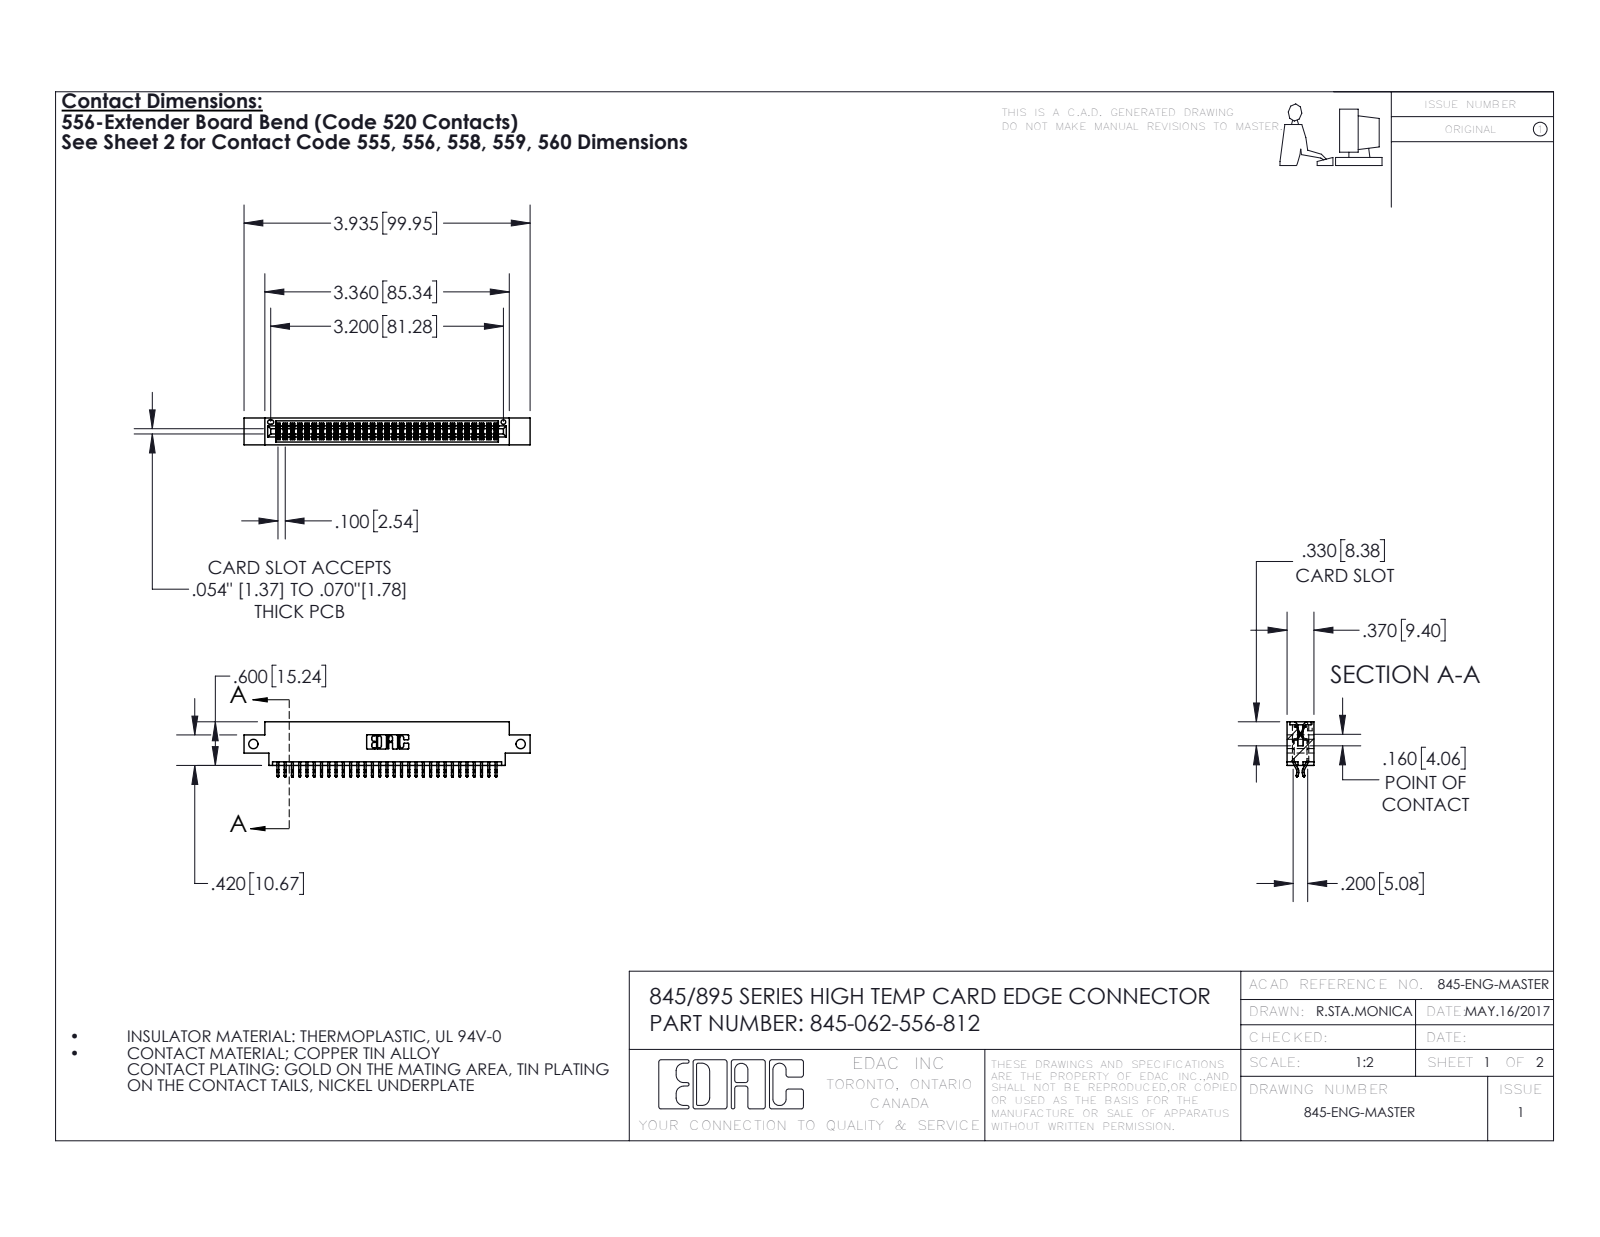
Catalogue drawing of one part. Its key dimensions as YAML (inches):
part_name: "345-292-001_556 Tail; 345-062-556-812; 345 Part_0.170 Offset - Side Mount"
step_written_by: "SolidWorks 2016 (CONFIG_CONTROL_DESIGN)"
units: inches
bodies: {solids: 63, faces: 3602, planar: 2378, cylindrical: 1224, other: 0}
overall_size: [3.935, 0.757, 0.37]
volume: 0.574
surface_area: 21.14
round_holes:
  - {diameter: 0.128, count: 2}
  - {diameter: 0.064, count: 1}
partial_cylinders:
  - {radius: 0.006, count: 94}
  - {radius: 0.01, count: 22}
  - {radius: 0.007, count: 6}
  - {radius: 0.031, count: 6}
  - {radius: 0.026, count: 3}
  - {radius: 0.01, count: 2}
  - {radius: 0.014, count: 2}
  - {radius: 0.019, count: 2}
face_to_face_distances: [0.298, 0.072, 0.37, 0.2, 0.025, 0.098, 0.272, 0.225, 0.175, 0.149]
hole_center_spacings: [3.675]
